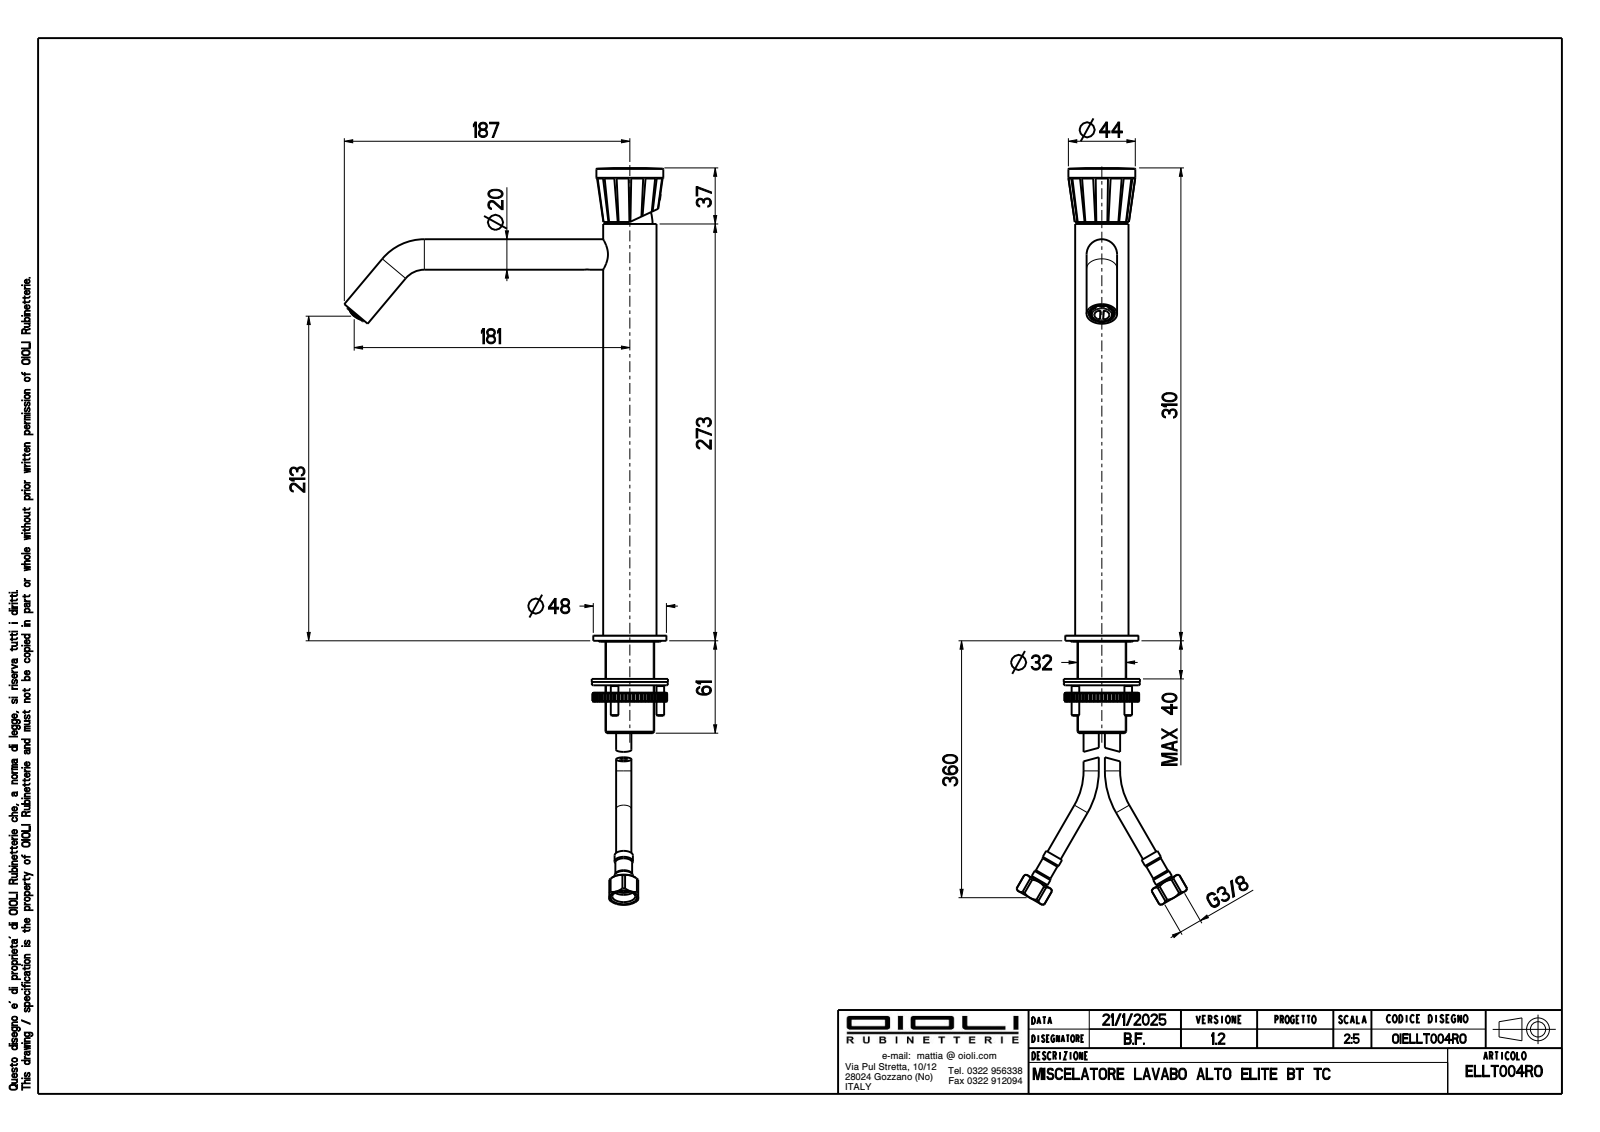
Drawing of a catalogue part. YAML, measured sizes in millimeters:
part_name: "OIBR00604; OICT00090; OIVT00002; OIAR00046 (+6 more)"
step_written_by: "CREO PARAMETRIC BY PTC INC, 2024493 (CONFIG_CONTROL_DESIGN)"
units: millimeters
bodies: {solids: 10, faces: 985, planar: 571, cylindrical: 184, other: 230}
overall_size: [310.18, 211.37, 48]
volume: 196640
surface_area: 91481
round_holes:
  - {diameter: 11, count: 3}
  - {diameter: 3.2, count: 2}
  - {diameter: 5, count: 2}
  - {diameter: 9, count: 2}
  - {diameter: 15, count: 2}
  - {diameter: 15.5, count: 2}
  - {diameter: 3.3, count: 1}
  - {diameter: 4, count: 1}
  - {diameter: 4.2, count: 1}
  - {diameter: 5.3, count: 1}
  - {diameter: 6.5, count: 1}
  - {diameter: 9.5, count: 1}
round_bosses_or_shafts:
  - {diameter: 20, count: 2}
  - {diameter: 16.5, count: 2}
  - {diameter: 10, count: 2}
  - {diameter: 48, count: 1}
  - {diameter: 43.9, count: 1}
  - {diameter: 35.6, count: 1}
  - {diameter: 35, count: 1}
  - {diameter: 32, count: 1}
partial_cylinders:
  - {radius: 0.1, count: 14}
  - {radius: 0.9, count: 8}
  - {radius: 0.6, count: 7}
  - {radius: 0.45, count: 3}
  - {radius: 2.5, count: 1}
  - {radius: 6.72, count: 1}
  - {radius: 7.46, count: 1}
  - {radius: 8.5, count: 1}
face_to_face_distances: [303.8, 3.4, 307.2, 123.4, 120, 183.8, 273.4, 270, 150, 33.8]
hole_center_spacings: [8.06, 2.37, 6.72, 8.94, 9.33, 11.77, 15.46, 17]
